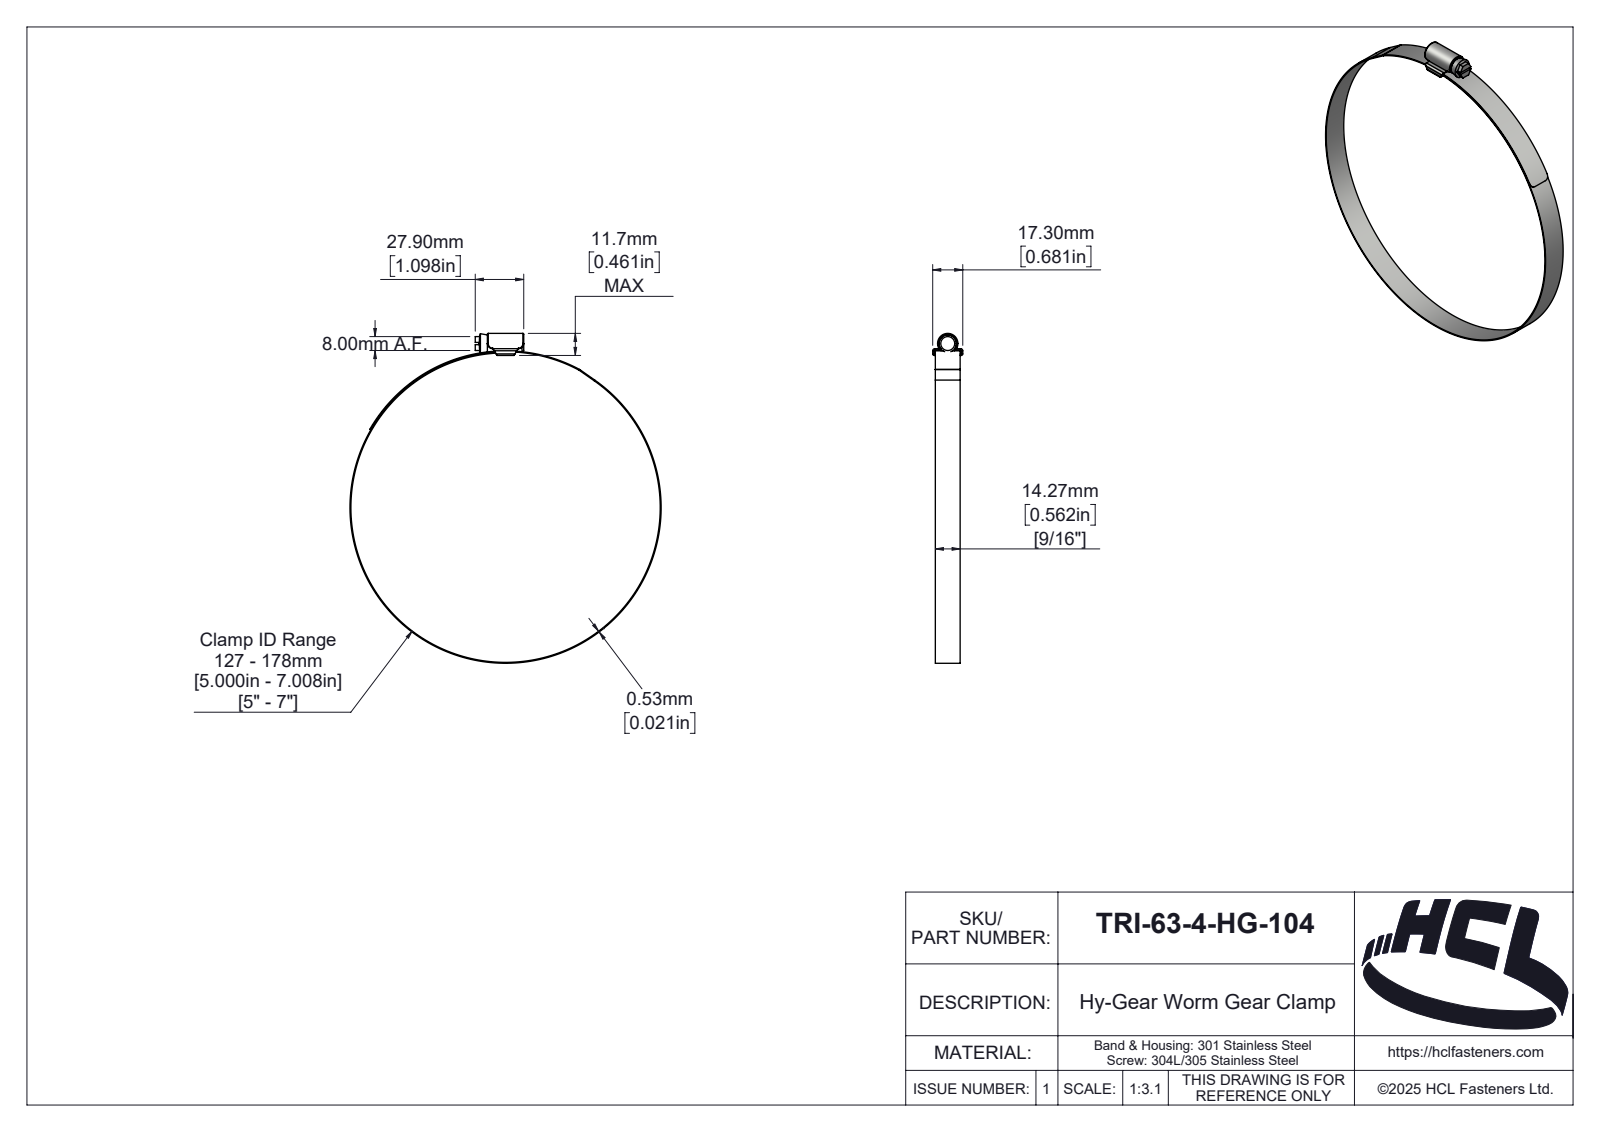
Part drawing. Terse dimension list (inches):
name: TRI-50-0-HG-104
written by: SolidWorks 2025 (AUTOMOTIVE_DESIGN)
unit: in
bodies: 3 solids, 189 faces (39 planar, 89 cylindrical, 61 other)
size: 7.47 × 7.05 × 0.681
volume: 0.473 in³; area: 34.41 in²
holes: 1× ⌀7.008
bosses: 1× ⌀7.05, 1× ⌀0.394
rounds: 6× R0.02, 4× R0.118, 2× R0.004, 2× R0.035, 2× R0.047, 1× R0.018, 1× R0.074, 1× R0.079
face distances: 0.561, 0.031, 0.122, 0.021, 0.091, 0.154, 1.098, 0.06, 0.621, 0.65
